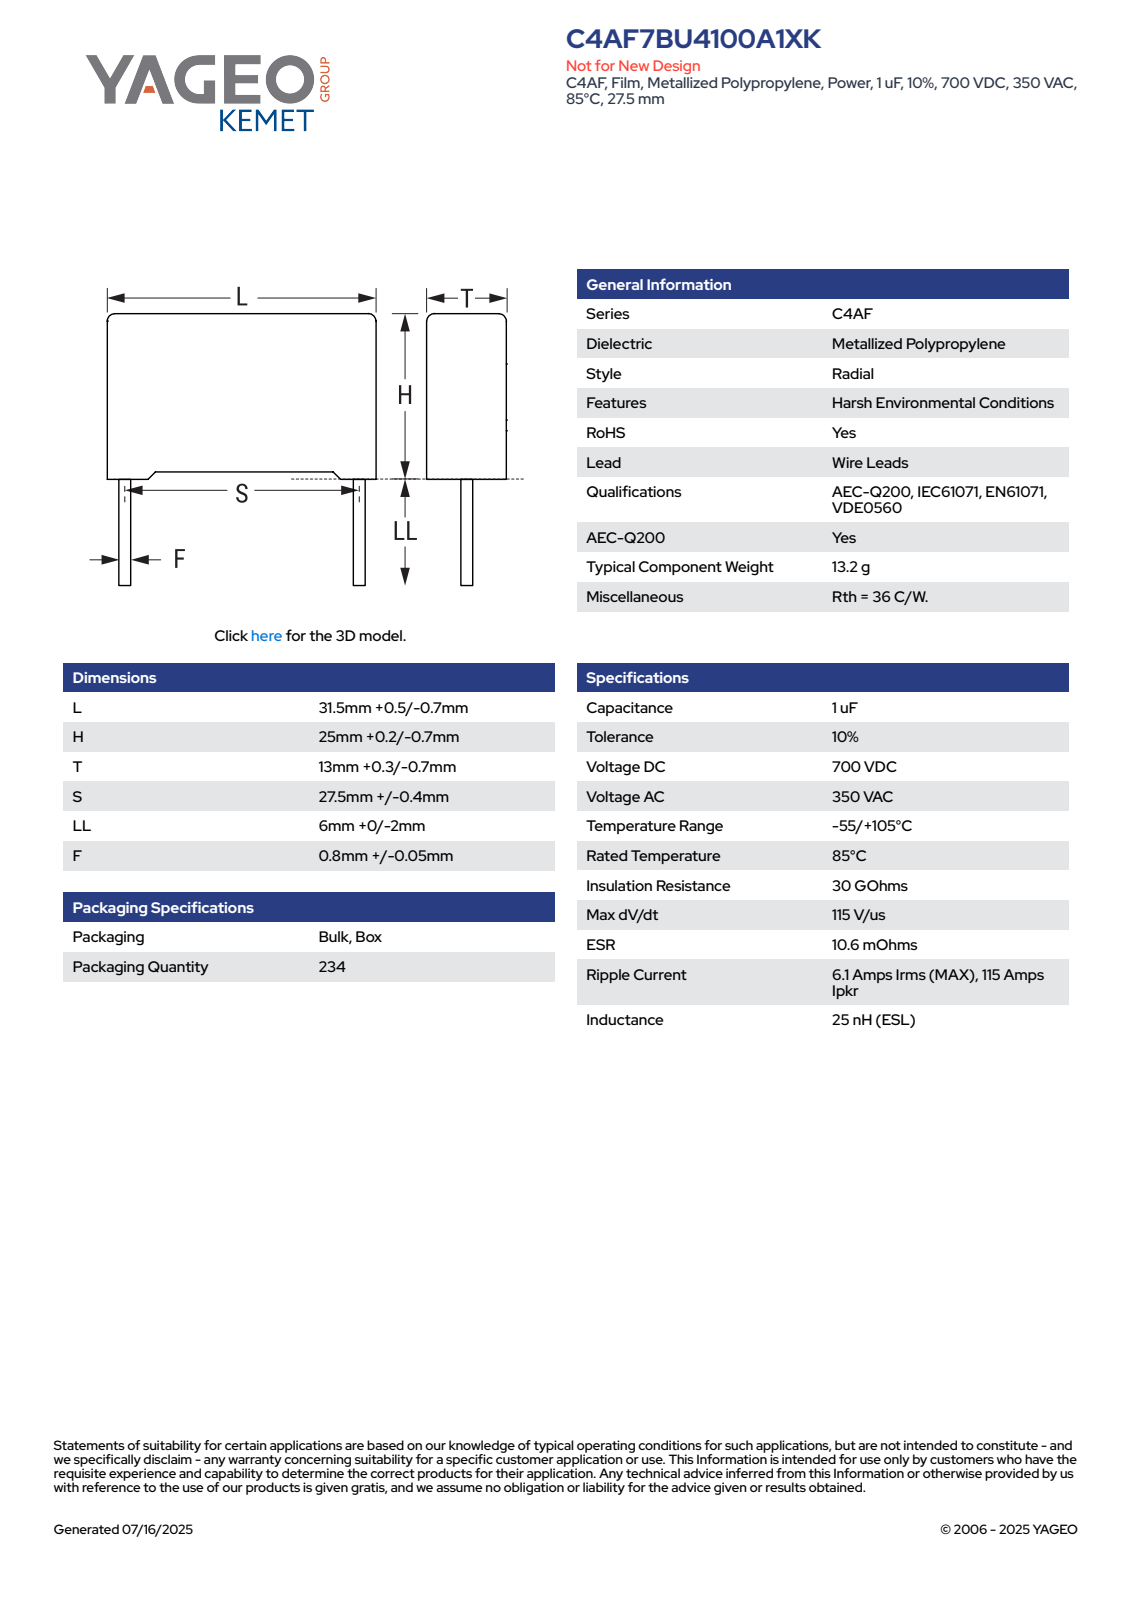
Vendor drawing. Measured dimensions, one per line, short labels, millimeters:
name: CFR_RB2CFP_31.5X25X13_L32H25.2T13.3S27.5LL6F0.85
written by: SolidWorks 2014 (AUTOMOTIVE_DESIGN)
unit: mm
bodies: 4 solids, 85 faces (77 planar, 8 cylindrical, 0 other)
size: 32 × 31.2 × 13.3
volume: 10 404 mm³; area: 3 215 mm²
bosses: 2× ⌀0.85
rounds: 4× R0.5
face distances: 13.3, 32, 24.33, 24.45, 0.87, 0.75, 25.2, 1.07, 13.31, 30.93
